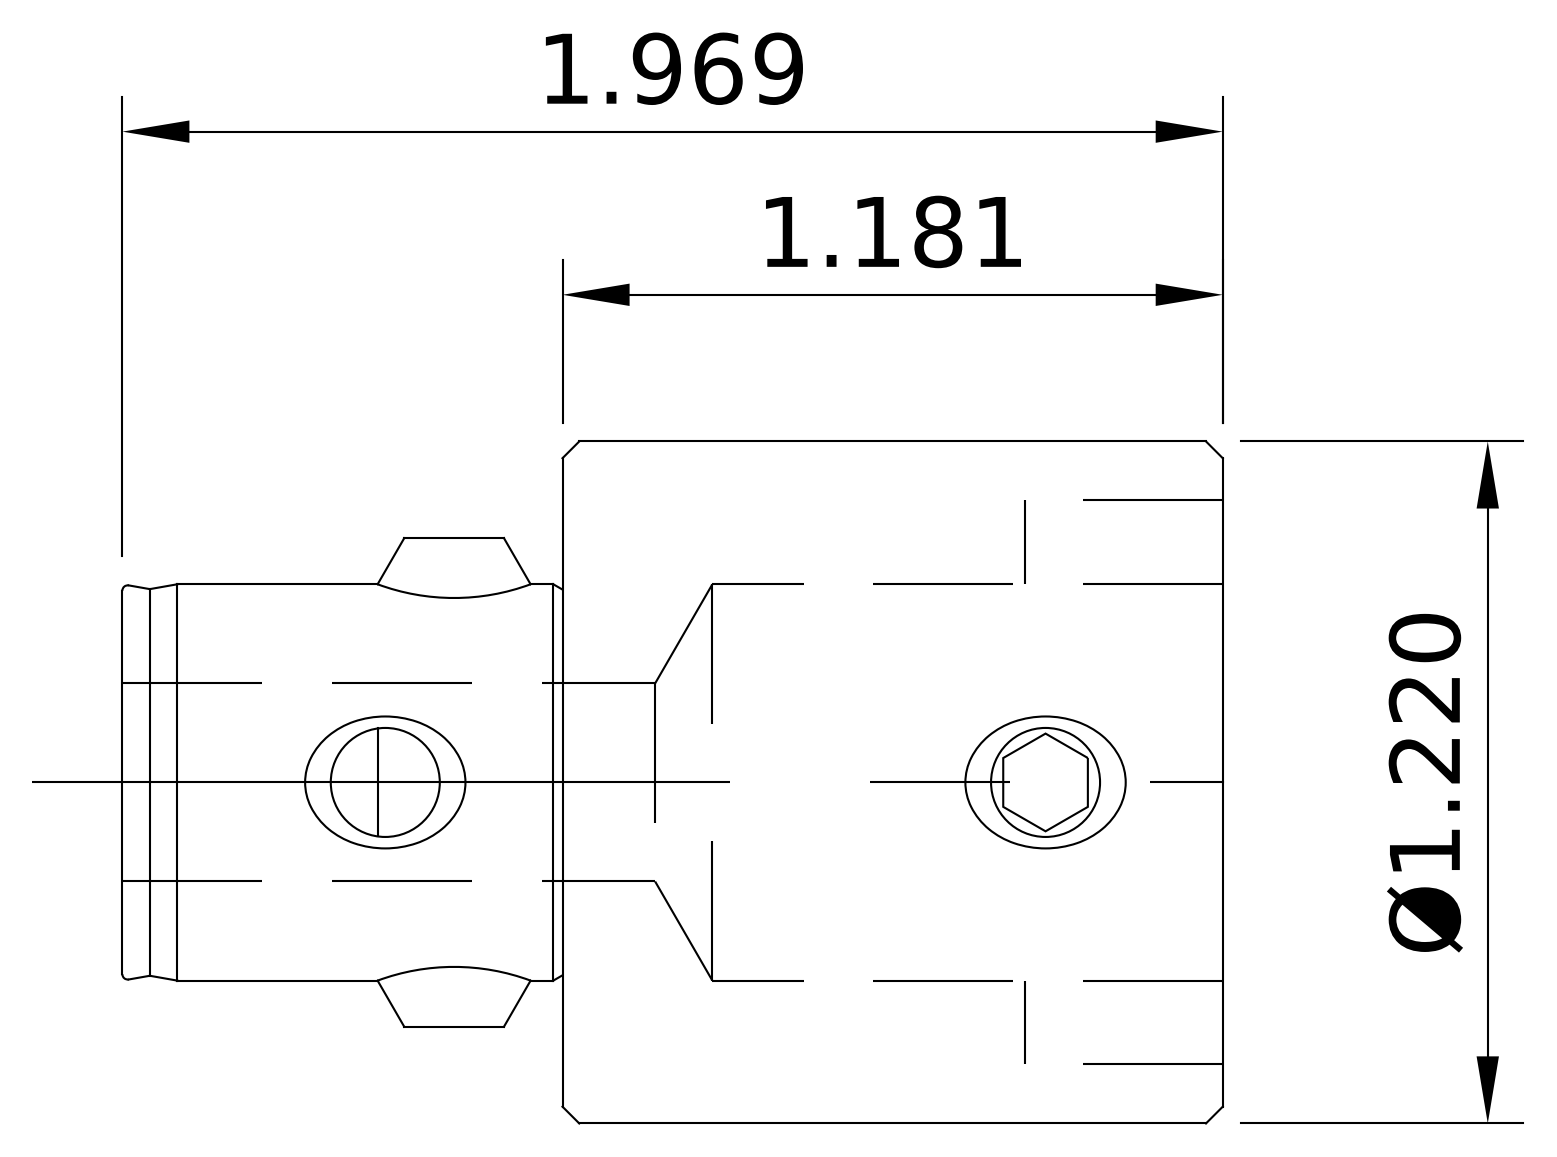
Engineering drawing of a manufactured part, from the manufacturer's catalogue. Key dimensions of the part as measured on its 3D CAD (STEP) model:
Part name (STEP PRODUCT): 11.331.330_11.331.330; 10.691.50X_10.691.503; 10.690.43X_10.690.433; 11.331.330 (+1 more)
STEP written by: SolidWorks 2016 (AUTOMOTIVE_DESIGN)
Units: millimetres
Bodies: 4 solids, 122 faces (35 planar, 40 cylindrical, 47 other)
Overall size (bounding box): 50 × 31 × 31
Volume: 19 893 mm³ · Surface area: 8 455 mm²
Round holes (diameter × count): ⌀5 ×2, ⌀4.5 ×1, ⌀6.2 ×1, ⌀7 ×1, ⌀9 ×1, ⌀18 ×1, ⌀18.5 ×1
Round bosses / shafts (diameter × count): ⌀31 ×1, ⌀6.9 ×1, ⌀6 ×1, ⌀4 ×1
Partial cylindrical surfaces — rounded edges, fillets, slot ends (radius × count): R2.75 ×2, R9 ×1
Main face-to-face distances: 30, 20, 50, 15.54, 41.1, 21.1, 8.9, 1, 2, 3.1
Hole centre spacings: 29.7
